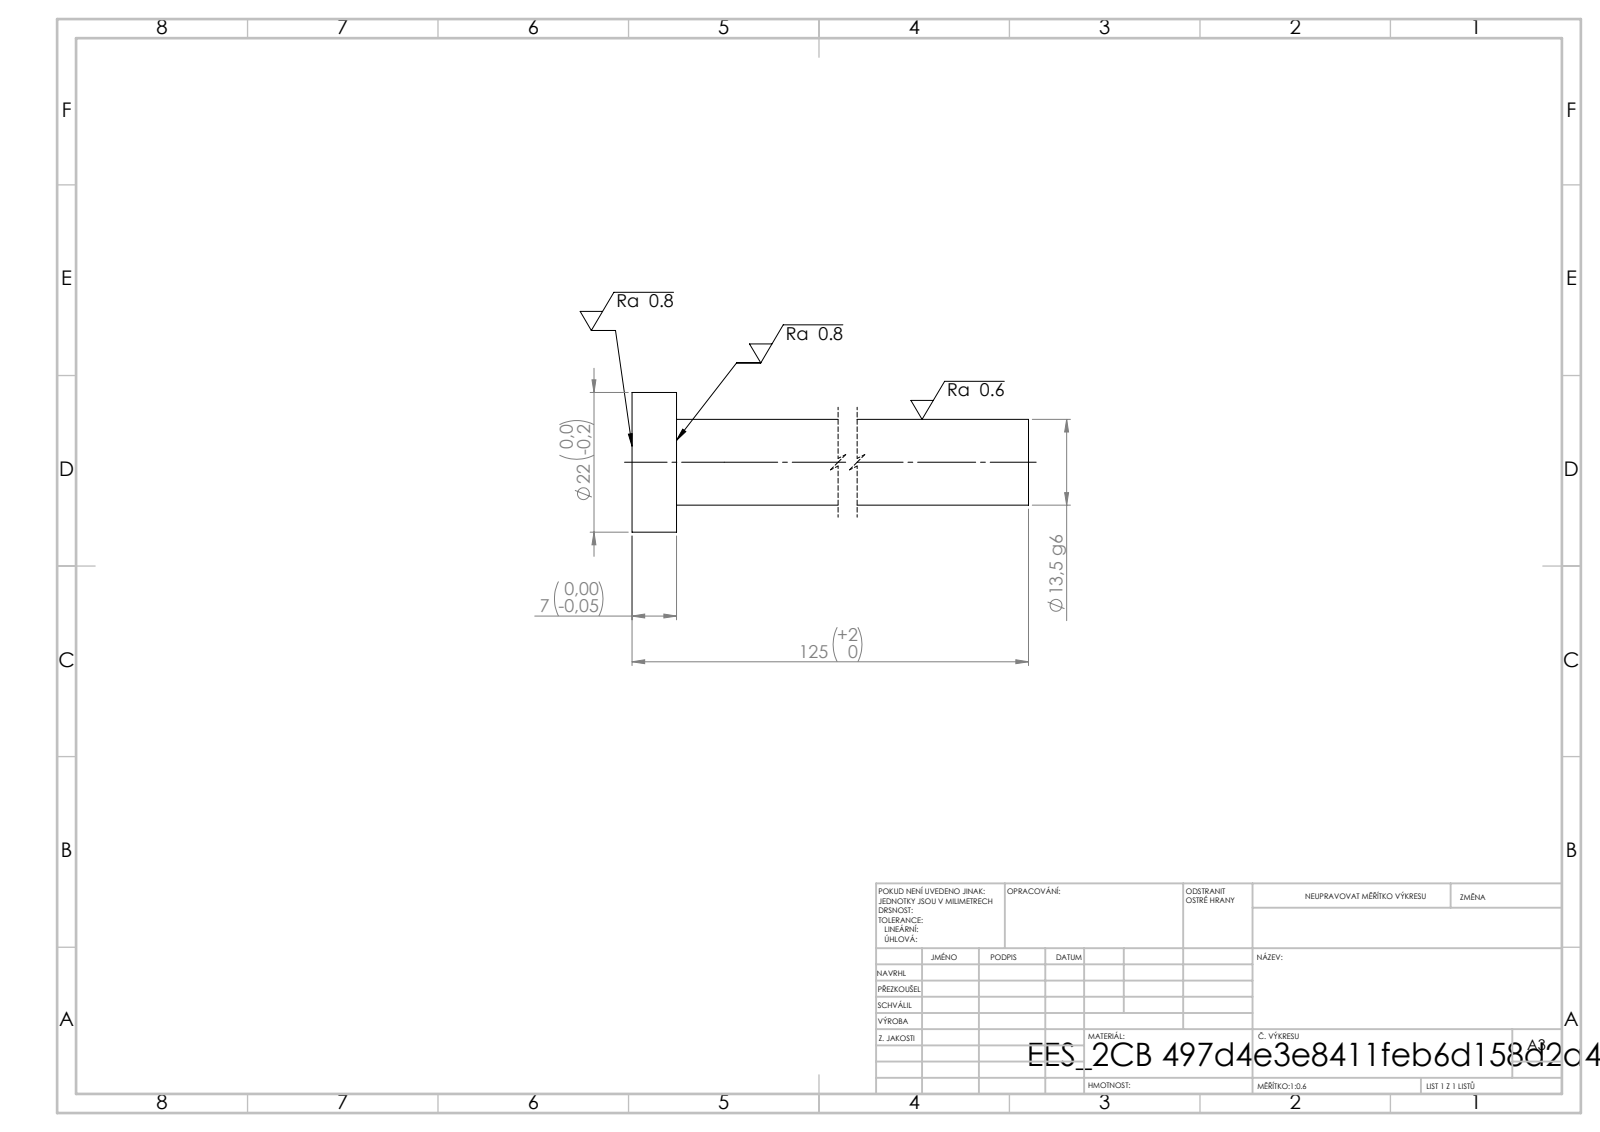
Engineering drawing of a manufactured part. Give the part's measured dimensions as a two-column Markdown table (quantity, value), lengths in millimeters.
| quantity | value |
| --- | --- |
| STEP written by | SolidWorks 2019 (CONFIG_CONTROL_DESIGN) |
| units | millimeters |
| bodies | 1 solid, 7 faces (3 planar, 4 cylindrical, 0 other) |
| overall size | 125 × 22 × 22 |
| volume | 19 551 mm³ |
| surface area | 6 249 mm² |
| round bosses / shafts (diameter × count) | 22 × 1, 13.5 × 1 |
| main face-to-face distances | 7, 125, 118 |
